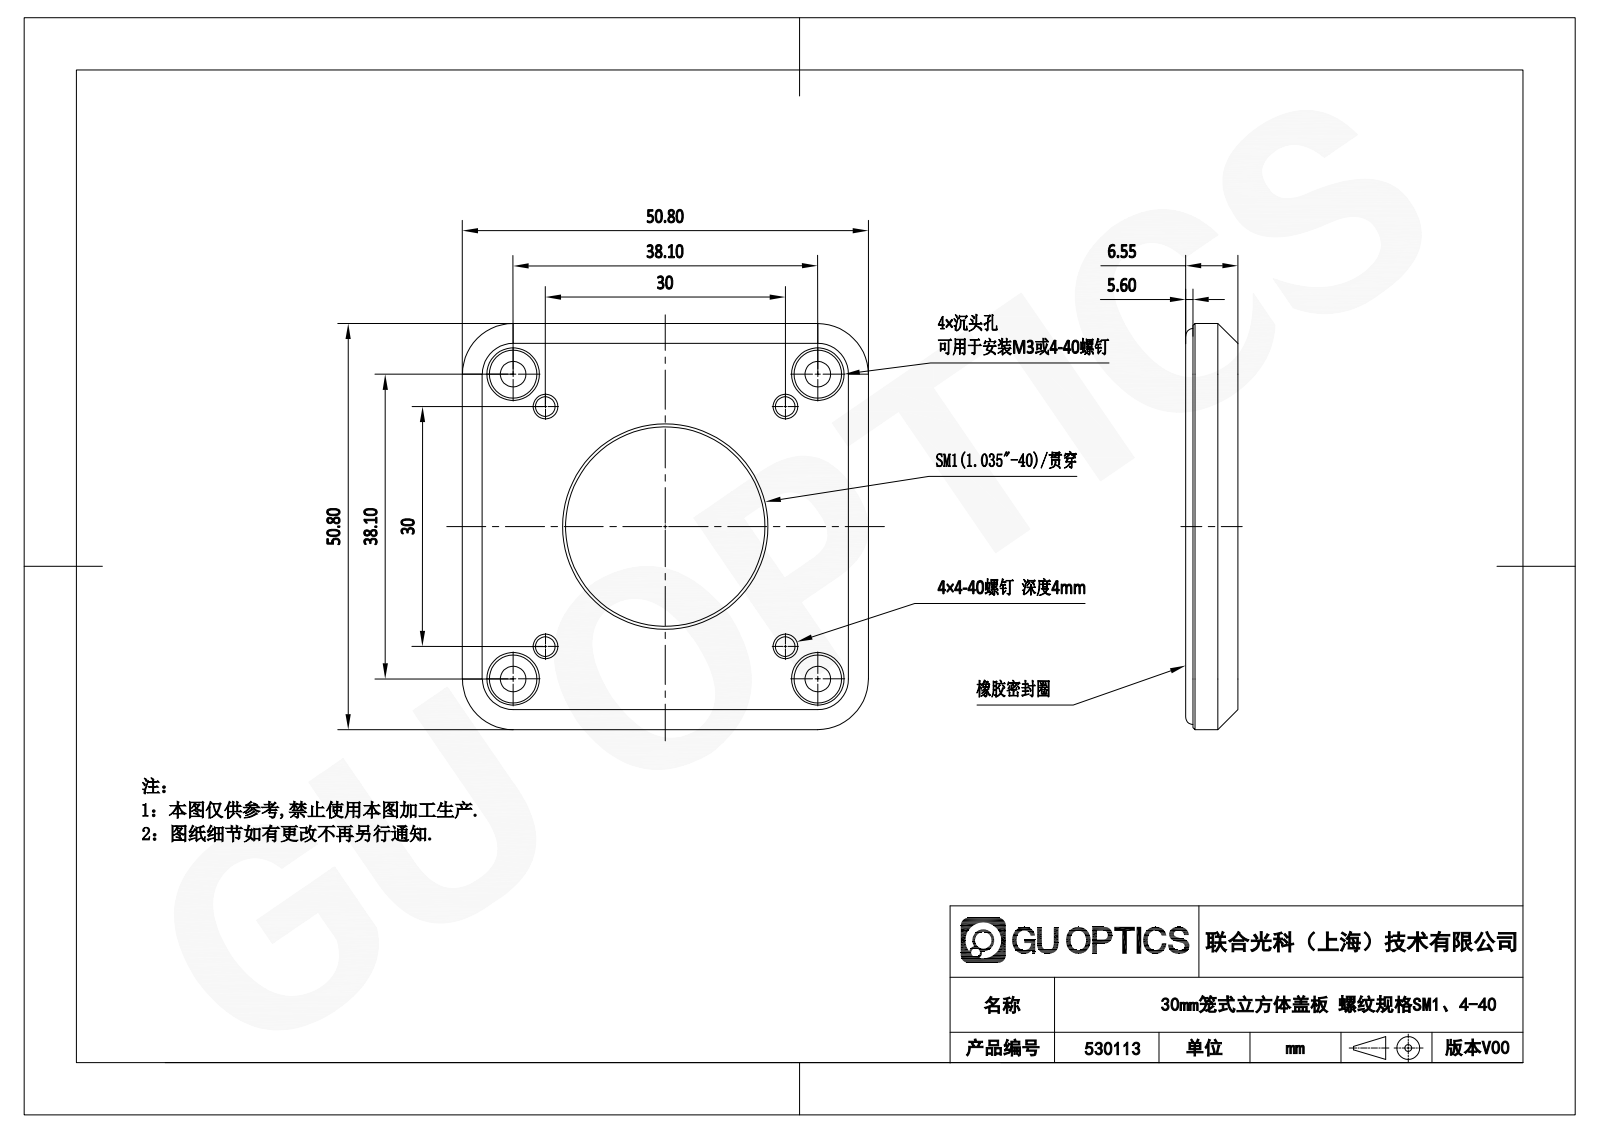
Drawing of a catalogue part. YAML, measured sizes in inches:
part_name: "530113"
step_written_by: "SolidWorks 2020 (CONFIG_CONTROL_DESIGN)"
units: inches
bodies: {solids: 2, faces: 58, planar: 20, cylindrical: 19, other: 19}
overall_size: [2, 2, 0.258]
volume: 0.623
surface_area: 10.82
round_holes:
  - {diameter: 0.089, count: 4}
  - {diameter: 0.126, count: 4}
  - {diameter: 0.236, count: 4}
  - {diameter: 1.01, count: 1}
  - {diameter: 1.95, count: 1}
round_bosses_or_shafts:
  - {diameter: 1.8, count: 1}
partial_cylinders:
  - {radius: 0.25, count: 4}
face_to_face_distances: [0.22, 0.161, 0.06, 2, 0.126, 0.035, 0.094, 1.493]
hole_center_spacings: [1.35, 0.226, 0.835, 1.061, 1.181, 1.5, 1.896, 1.67]
